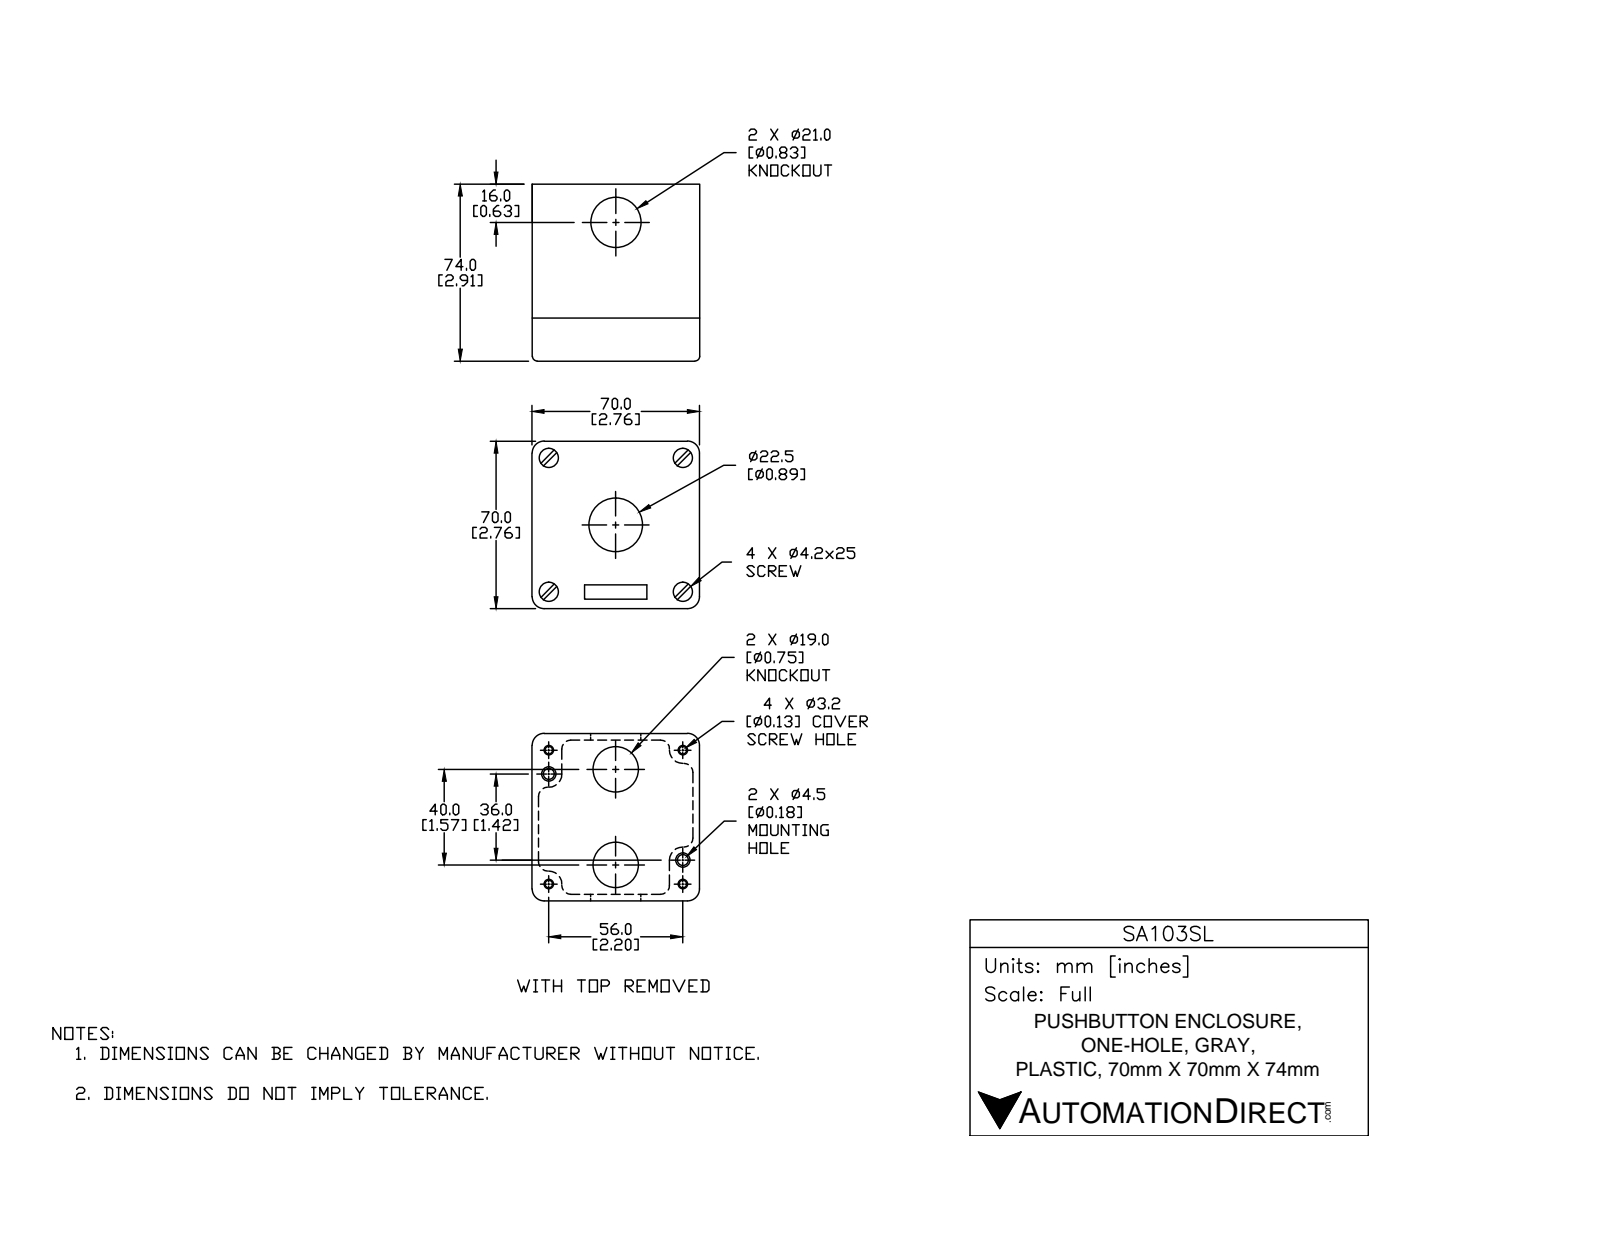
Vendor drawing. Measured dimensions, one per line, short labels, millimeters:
name: SA103SL
written by: SolidWorks 2018 (AUTOMOTIVE_DESIGN)
unit: mm
bodies: 6 solids, 449 faces (121 planar, 178 cylindrical, 150 other)
size: 74.2 × 70 × 70
volume: 116 400 mm³; area: 61 350 mm²
holes: 4× ⌀3.2, 4× ⌀4.2, 4× ⌀8, 2× ⌀4.5, 2× ⌀7.5, 2× ⌀19, 1× ⌀21, 1× ⌀22.5
bosses: 4× ⌀7.4, 4× ⌀2.8
rounds: 16× R0.5, 8× R1, 8× R2.4, 4× R1, 4× R1.8, 4× R5, 4× R6.6, 4× R8.2
face distances: 70, 67.4, 2.6, 74, 64.8, 2.2, 71.9, 2, 72.1, 69.9
hole spacings: 29.1, 39.6, 55.6, 56, 10, 20, 28.1, 33.3
